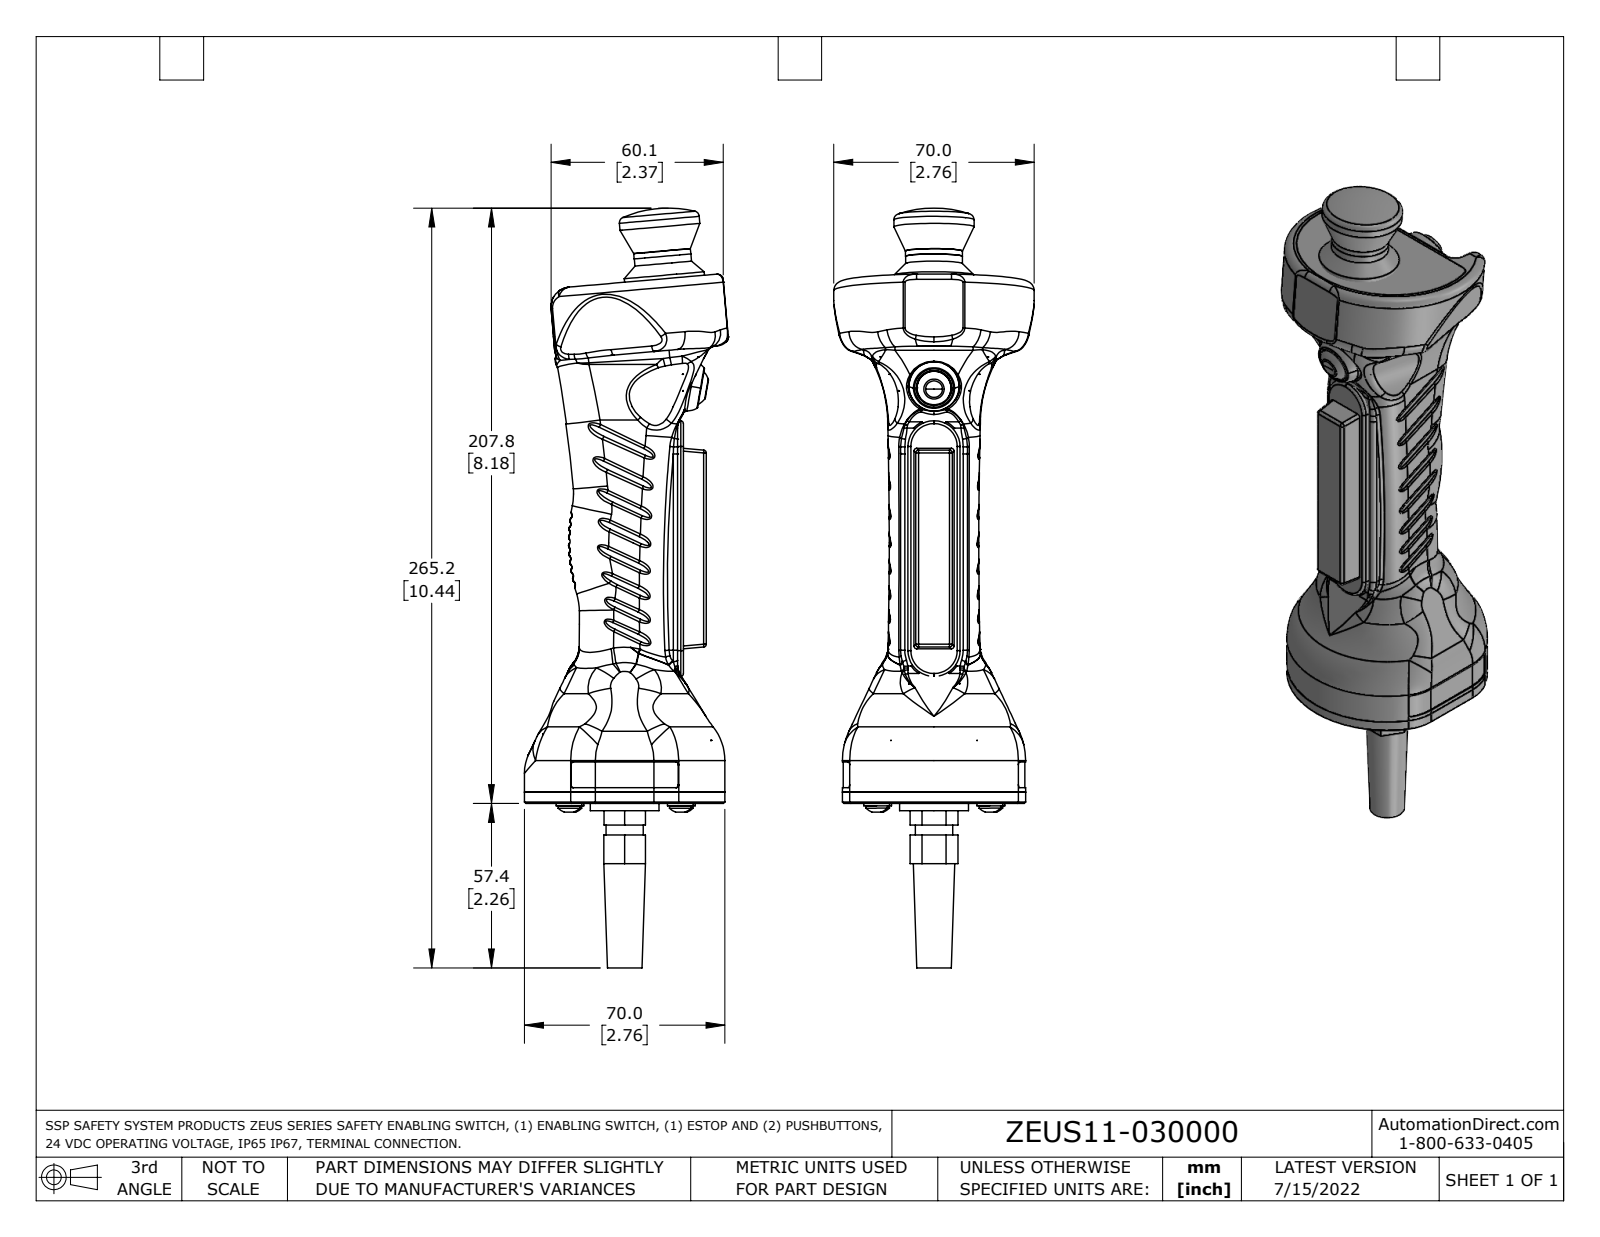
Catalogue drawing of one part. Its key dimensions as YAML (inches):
part_name: "ZEUS11-030000"
step_written_by: "SolidWorks 2021 (AUTOMOTIVE_DESIGN)"
units: inches
bodies: {solids: 22, faces: 1618, planar: 631, cylindrical: 511, other: 476}
overall_size: [10.442, 2.803, 2.756]
volume: 24.32
surface_area: 131.7
round_holes:
  - {diameter: 0.132, count: 4}
  - {diameter: 0.169, count: 4}
  - {diameter: 0.177, count: 4}
  - {diameter: 0.197, count: 4}
  - {diameter: 0.039, count: 2}
  - {diameter: 0.098, count: 2}
  - {diameter: 0.11, count: 2}
  - {diameter: 0.159, count: 2}
  - {diameter: 0.165, count: 2}
  - {diameter: 0.201, count: 2}
  - {diameter: 0.205, count: 2}
  - {diameter: 0.299, count: 2}
round_bosses_or_shafts:
  - {diameter: 0.354, count: 4}
  - {diameter: 0.295, count: 4}
  - {diameter: 0.157, count: 4}
  - {diameter: 0.039, count: 4}
  - {diameter: 0.461, count: 3}
  - {diameter: 1.102, count: 2}
  - {diameter: 0.781, count: 2}
  - {diameter: 0.689, count: 2}
partial_cylinders:
  - {radius: 0.005, count: 96}
  - {radius: 0.039, count: 51}
  - {radius: 0.028, count: 48}
  - {radius: 0.008, count: 42}
  - {radius: 0.079, count: 21}
  - {radius: 0.006, count: 16}
  - {radius: 0.118, count: 10}
  - {radius: 0.031, count: 7}
face_to_face_distances: [0.157, 0.079, 0.079, 0.014, 0.065, 0.02, 0.059, 0.039, 0.098, 0.177]
hole_center_spacings: [1.531, 0.404, 0.867, 1.181, 0.63, 1.558, 0.513, 0.513]
